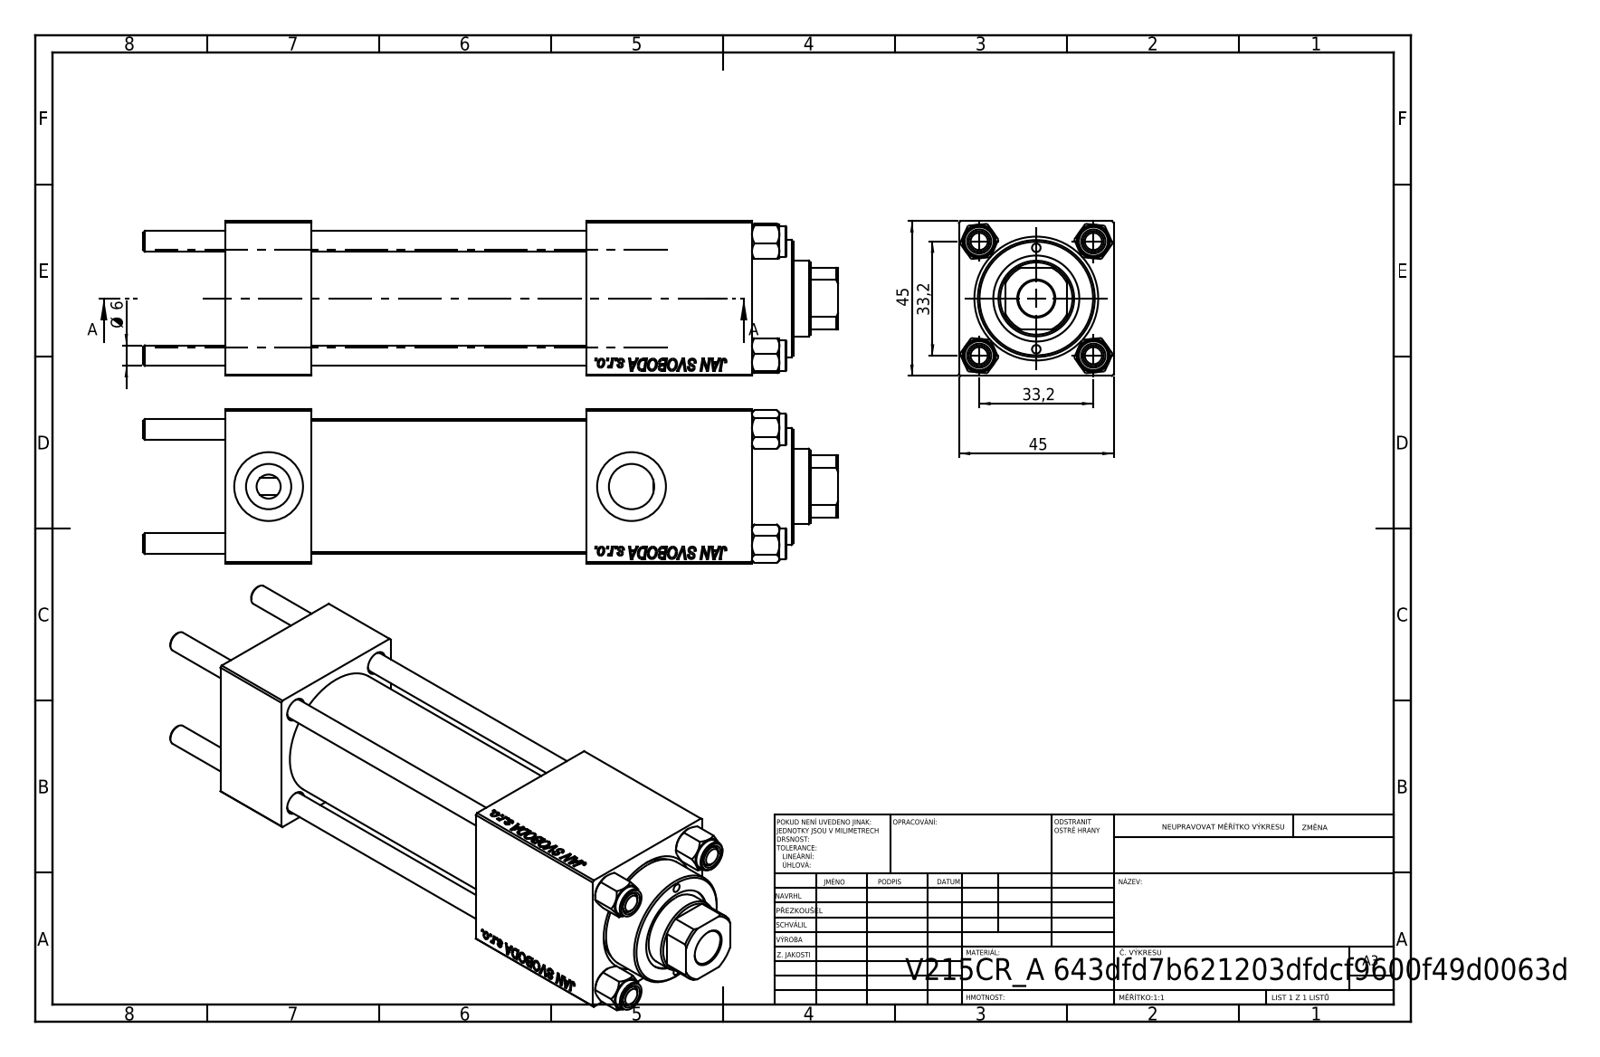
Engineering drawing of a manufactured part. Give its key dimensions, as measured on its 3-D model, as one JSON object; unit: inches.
{"part_name": "CR025_012_A_0_G_A_G_M_020_+#_##_TYCINKA; V215CR_BODY_A; V215CR_VCP; V215_VC_A (+1 more)", "step_written_by": "SolidWorks 2019 (CONFIG_CONTROL_DESIGN)", "units": "inches", "bodies": {"solids": 11, "faces": 1139, "planar": 521, "cylindrical": 82, "other": 536}, "overall_size": [7.953, 1.772, 1.772], "volume_in3": 14.57, "surface_area_in2": 136.8, "round_holes": [[0.236, 4], [0.098, 2], [0.276, 2], [0.518, 2], [0.787, 2], [0.413, 1], [0.866, 1], [0.945, 1], [0.984, 1], [1.26, 1], [1.299, 1]], "round_bosses_or_shafts": [[0.354, 4], [1.496, 1], [1.339, 1]], "partial_cylinders_radius": [[0.413, 1]], "face_to_face_distances": [1.772, 0.984, 6.024, 4.134, 3.15, 5.039, 1.89, 4.894, 3.909, 0.76], "hole_center_spacings": [0.657, 0.924, 1.307, 1.396, 0.581, 1.848, 1.161, 4.154]}
